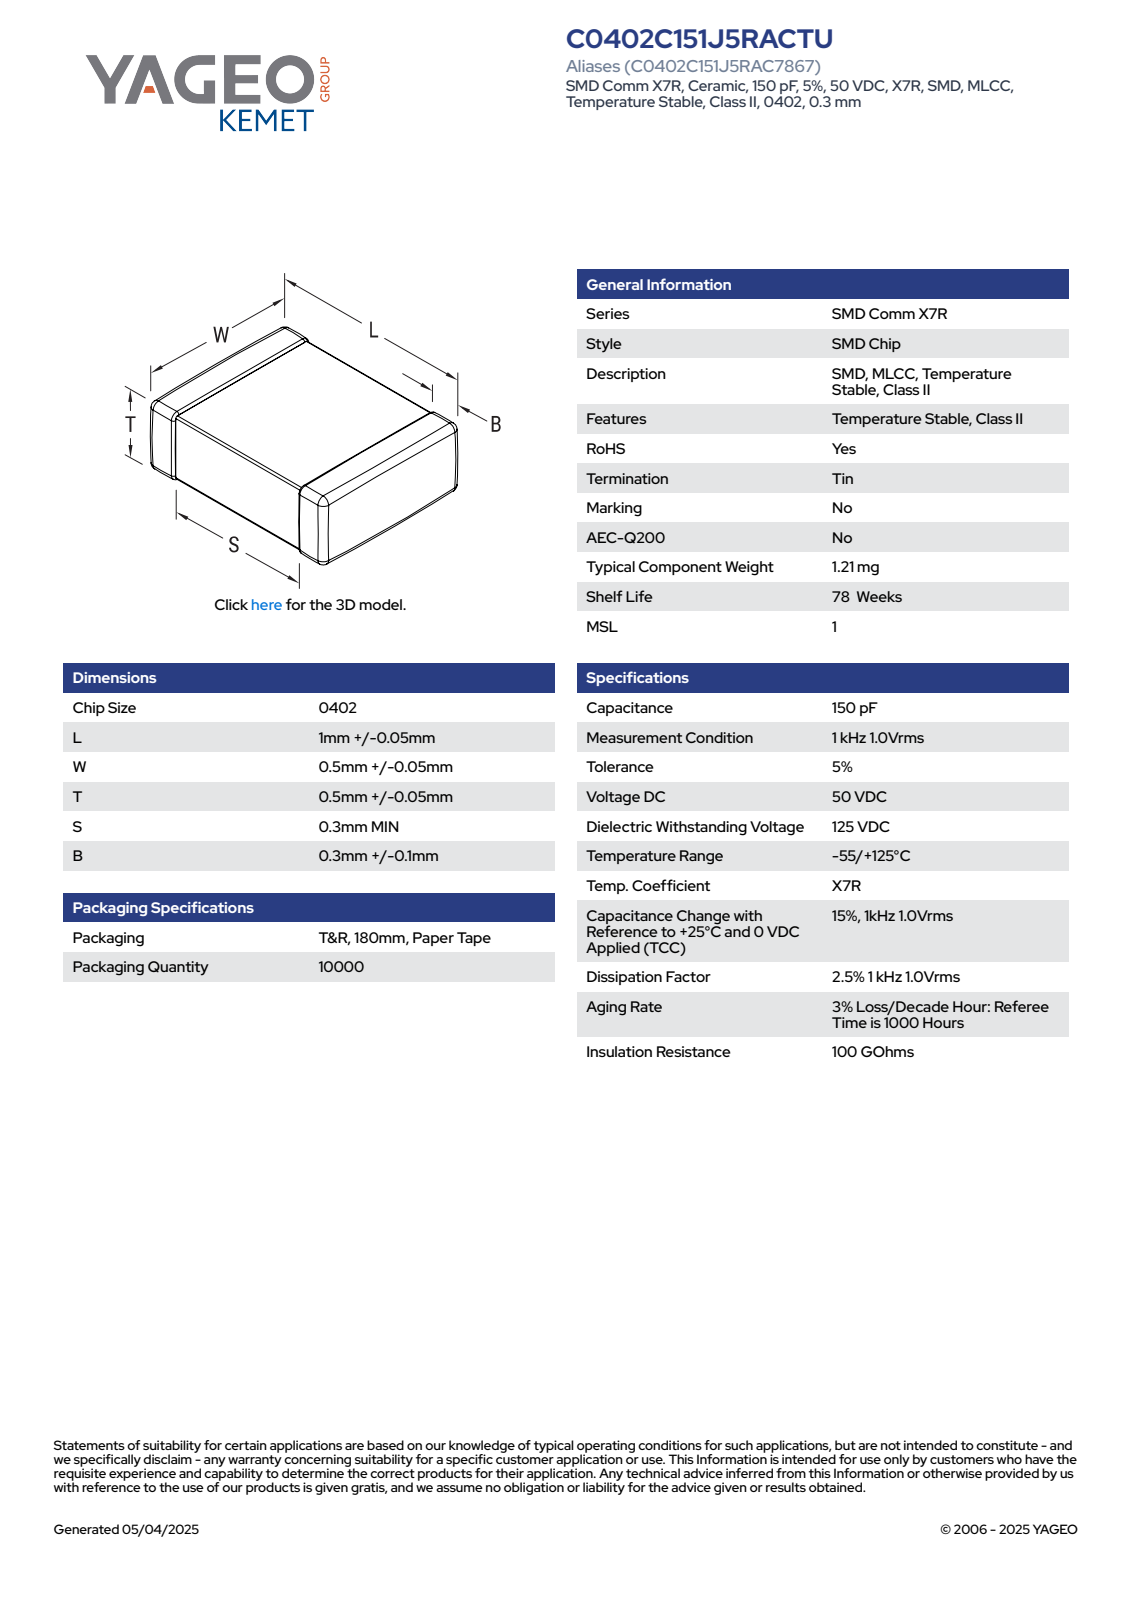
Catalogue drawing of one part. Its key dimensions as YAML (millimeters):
part_name: "CCS_CCSTD_0402_L1.05W0.55T0.55B0.3"
step_written_by: "SolidWorks 2021 (AUTOMOTIVE_DESIGN)"
units: millimeters
bodies: {solids: 4, faces: 125, planar: 71, cylindrical: 38, other: 16}
overall_size: [1.05, 0.55, 0.55]
volume: 0.311
surface_area: 3
face_to_face_distances: [0.55, 0.54, 1.05, 0.53, 0.49, 0.56, 0.57, 0.48, 0.5, 0.52]
